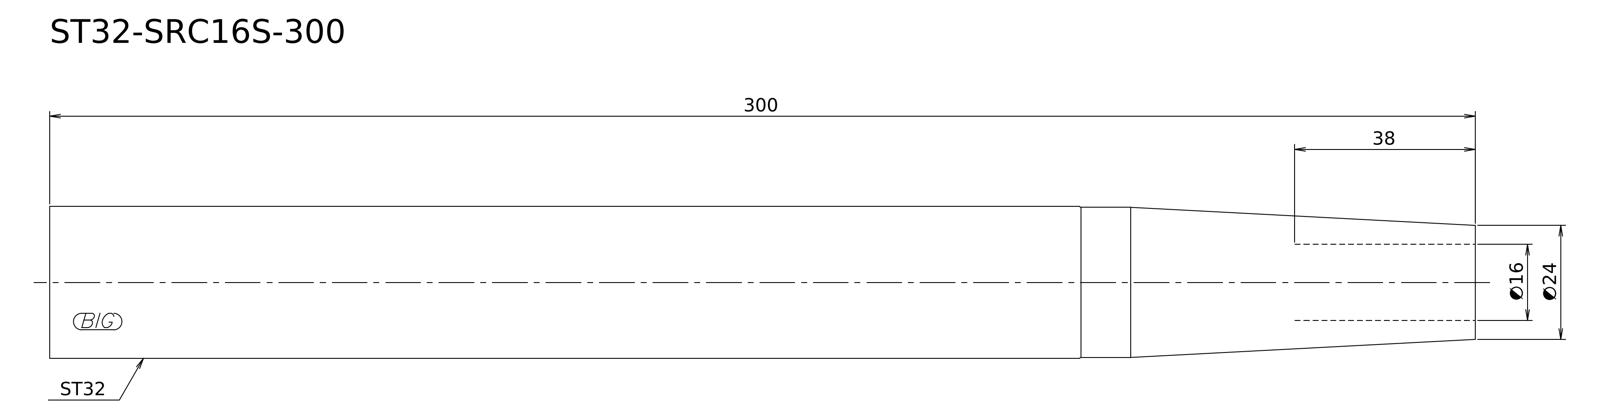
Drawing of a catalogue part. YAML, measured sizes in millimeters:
step_written_by: "Kubotek KeyCreator V8.5.1 (14335) (CONFIG_CONTROL_DESIGN)"
units: millimeters
bodies: {solids: 1, faces: 6, planar: 2, cylindrical: 2, other: 2}
overall_size: [300, 32, 32]
volume: 227032
surface_area: 30460
round_bosses_or_shafts:
  - {diameter: 32, count: 1}
  - {diameter: 31.6, count: 1}
face_to_face_distances: [300]
